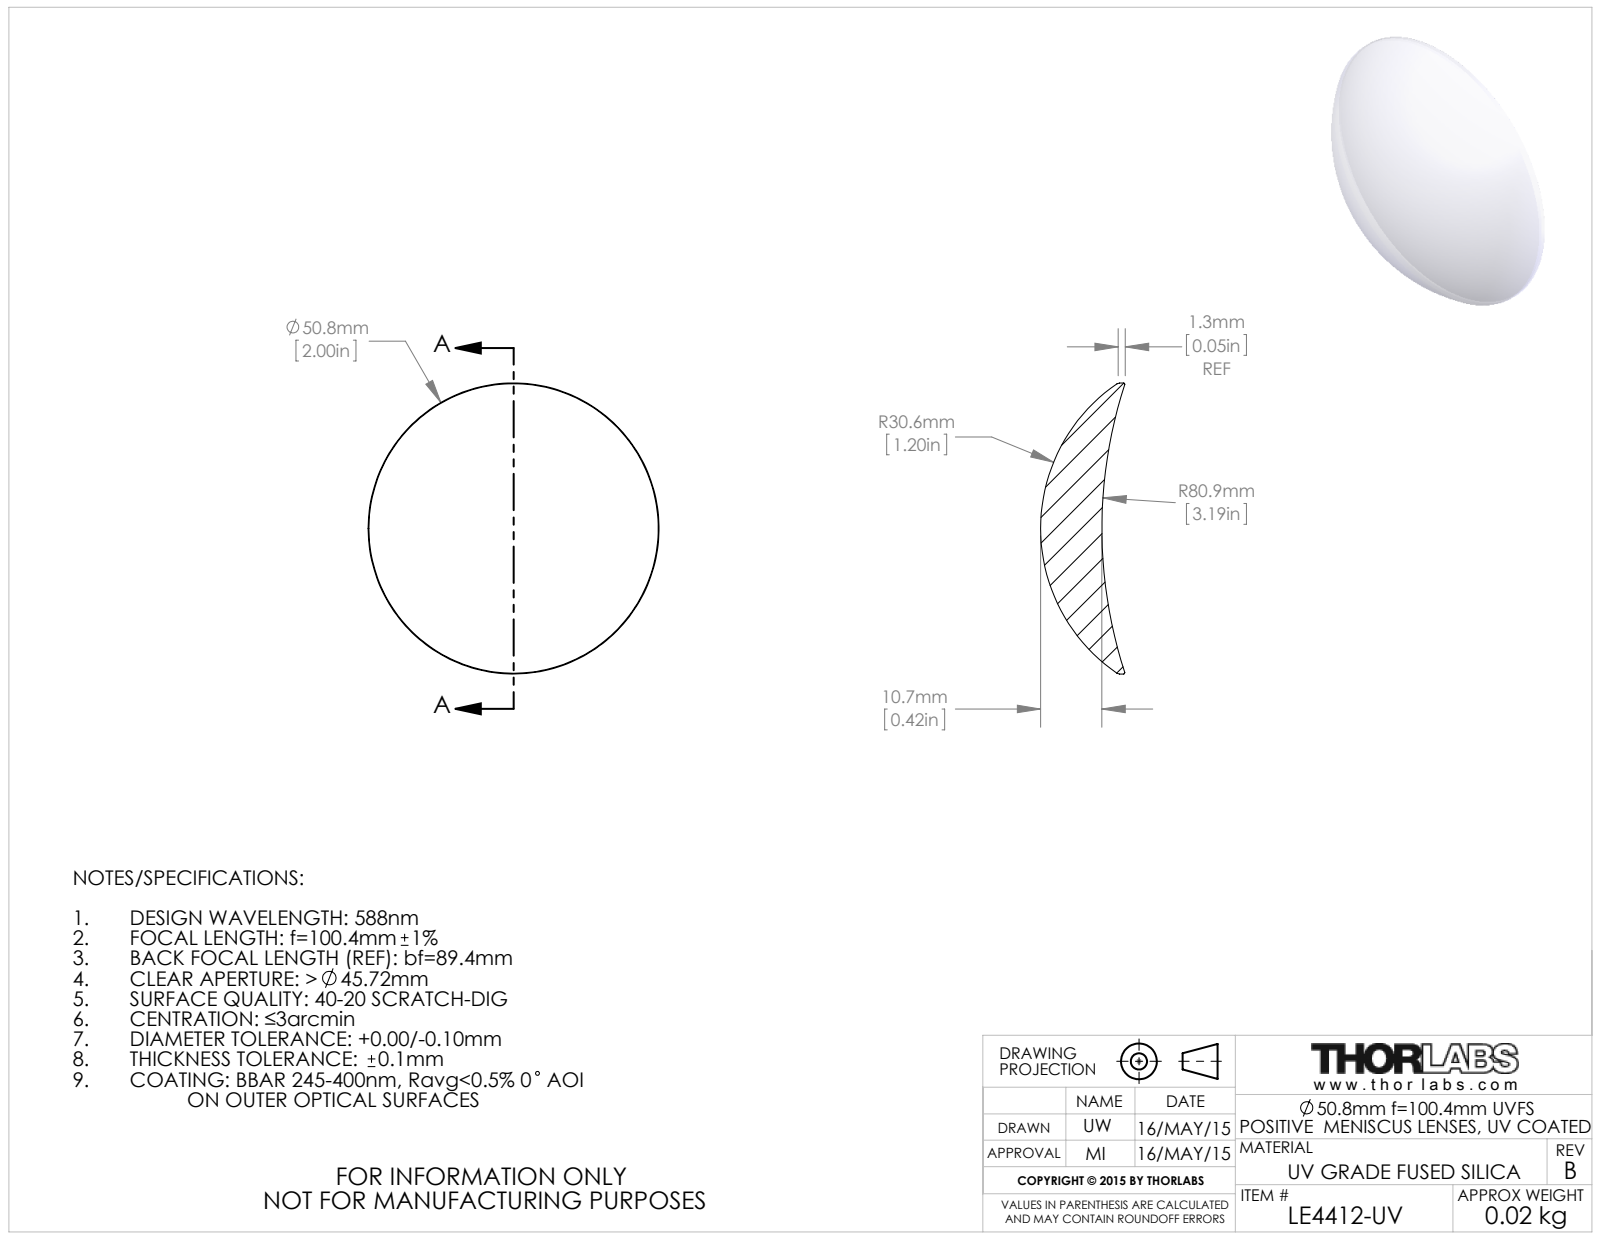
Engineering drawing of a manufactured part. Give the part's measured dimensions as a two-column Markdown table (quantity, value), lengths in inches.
| quantity | value |
| --- | --- |
| part name | 4931-E0W |
| STEP written by | SolidWorks 2014 (CONFIG_CONTROL_DESIGN) |
| units | inches |
| bodies | 1 solid, 10 faces (0 planar, 2 cylindrical, 8 other) |
| overall size | 2 × 2 × 0.579 |
| volume | 0.816 in³ |
| surface area | 7.511 in² |
| round bosses / shafts (diameter × count) | 2 × 1 |
